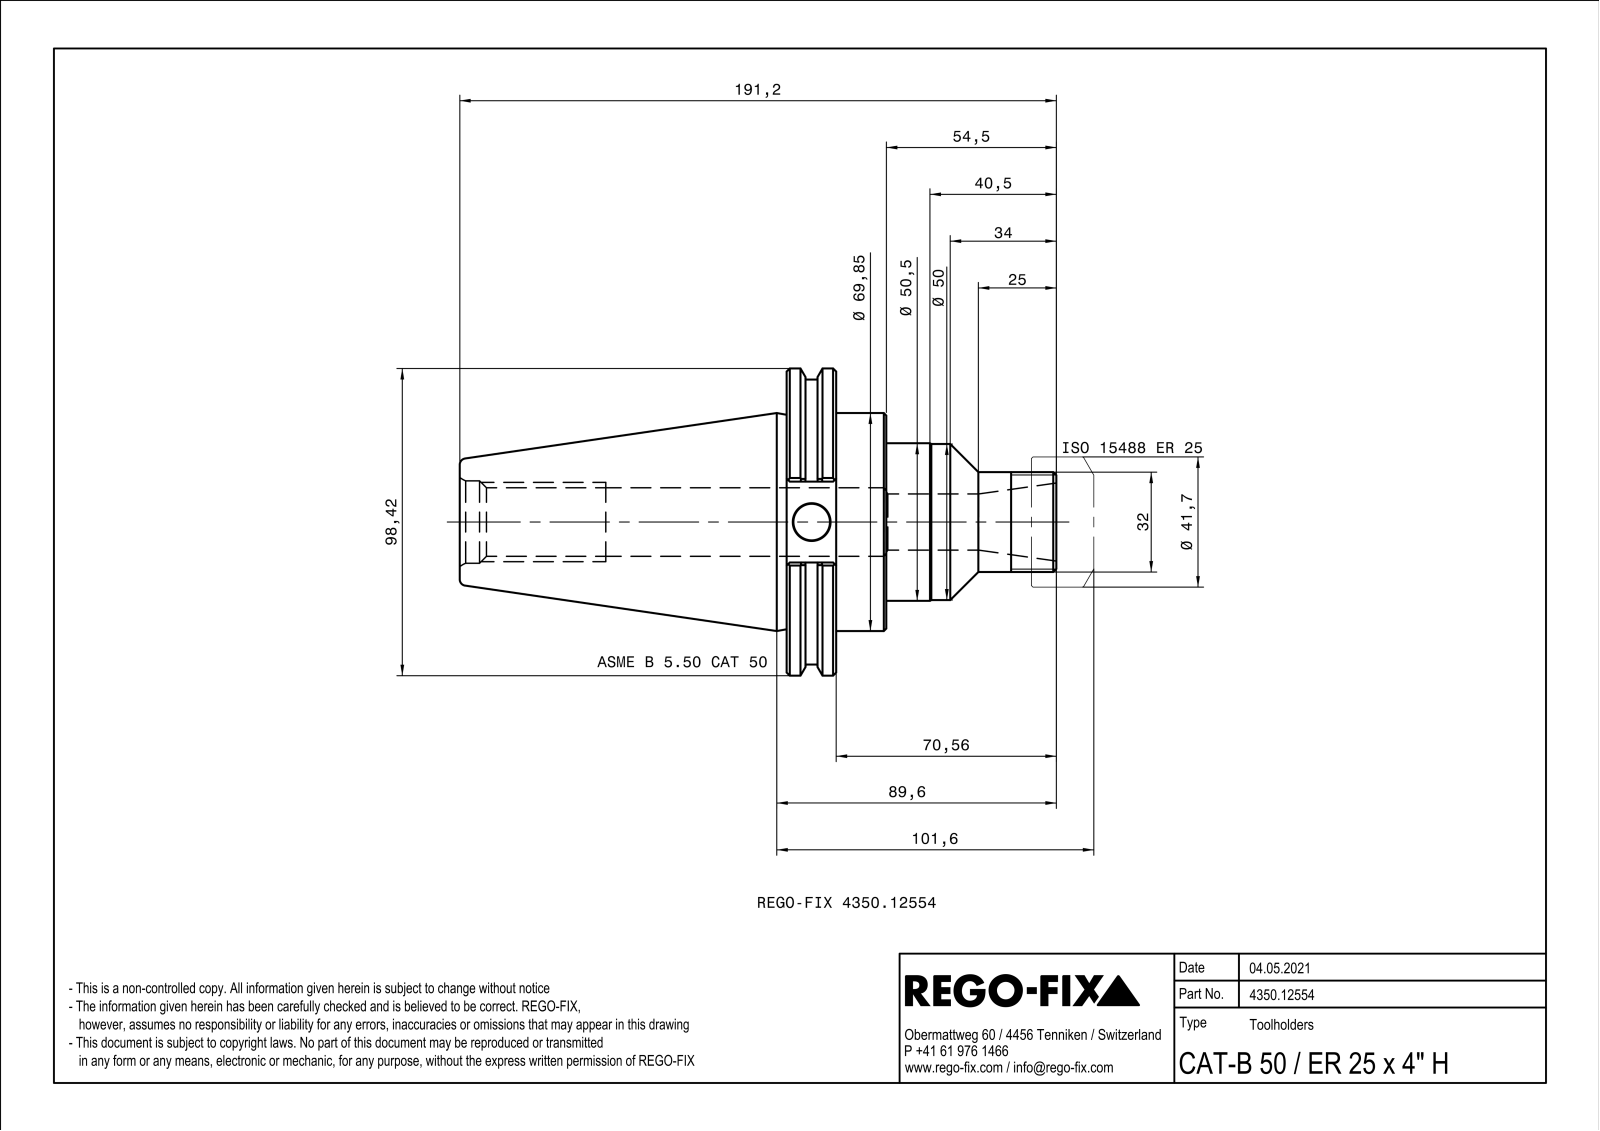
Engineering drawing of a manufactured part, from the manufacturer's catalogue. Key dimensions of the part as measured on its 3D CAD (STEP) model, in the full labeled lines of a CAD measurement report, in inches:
Part name (STEP PRODUCT): NOCUT
STEP written by: SIEMENS PLM Software Solid Edge ST10 (AUTOMOTIVE_DESIGN)
Units: inches
Bodies: 1 solid, 117 faces (35 planar, 41 cylindrical, 41 other)
Overall size (bounding box): 7.528 × 3.875 × 3.716
Volume: 26.08 in³ · Surface area: 91.25 in²
Round holes (diameter × count): ⌀0.128 ×2, ⌀0.154 ×2, ⌀0.461 ×1, ⌀0.709 ×1, ⌀0.865 ×1, ⌀0.865 ×1, ⌀1.039 ×1
Round bosses / shafts (diameter × count): ⌀3.875 ×1, ⌀3.594 ×1, ⌀2.75 ×1, ⌀1.988 ×1, ⌀1.969 ×1, ⌀1.26 ×1
Partial cylindrical surfaces — rounded edges, fillets, slot ends (radius × count): R0.02 ×12
Main face-to-face distances: 0.625, 0.632, 1.257, 5.382, 4.75, 4.125, 2.863, 1.02, 2.146, 2.778
